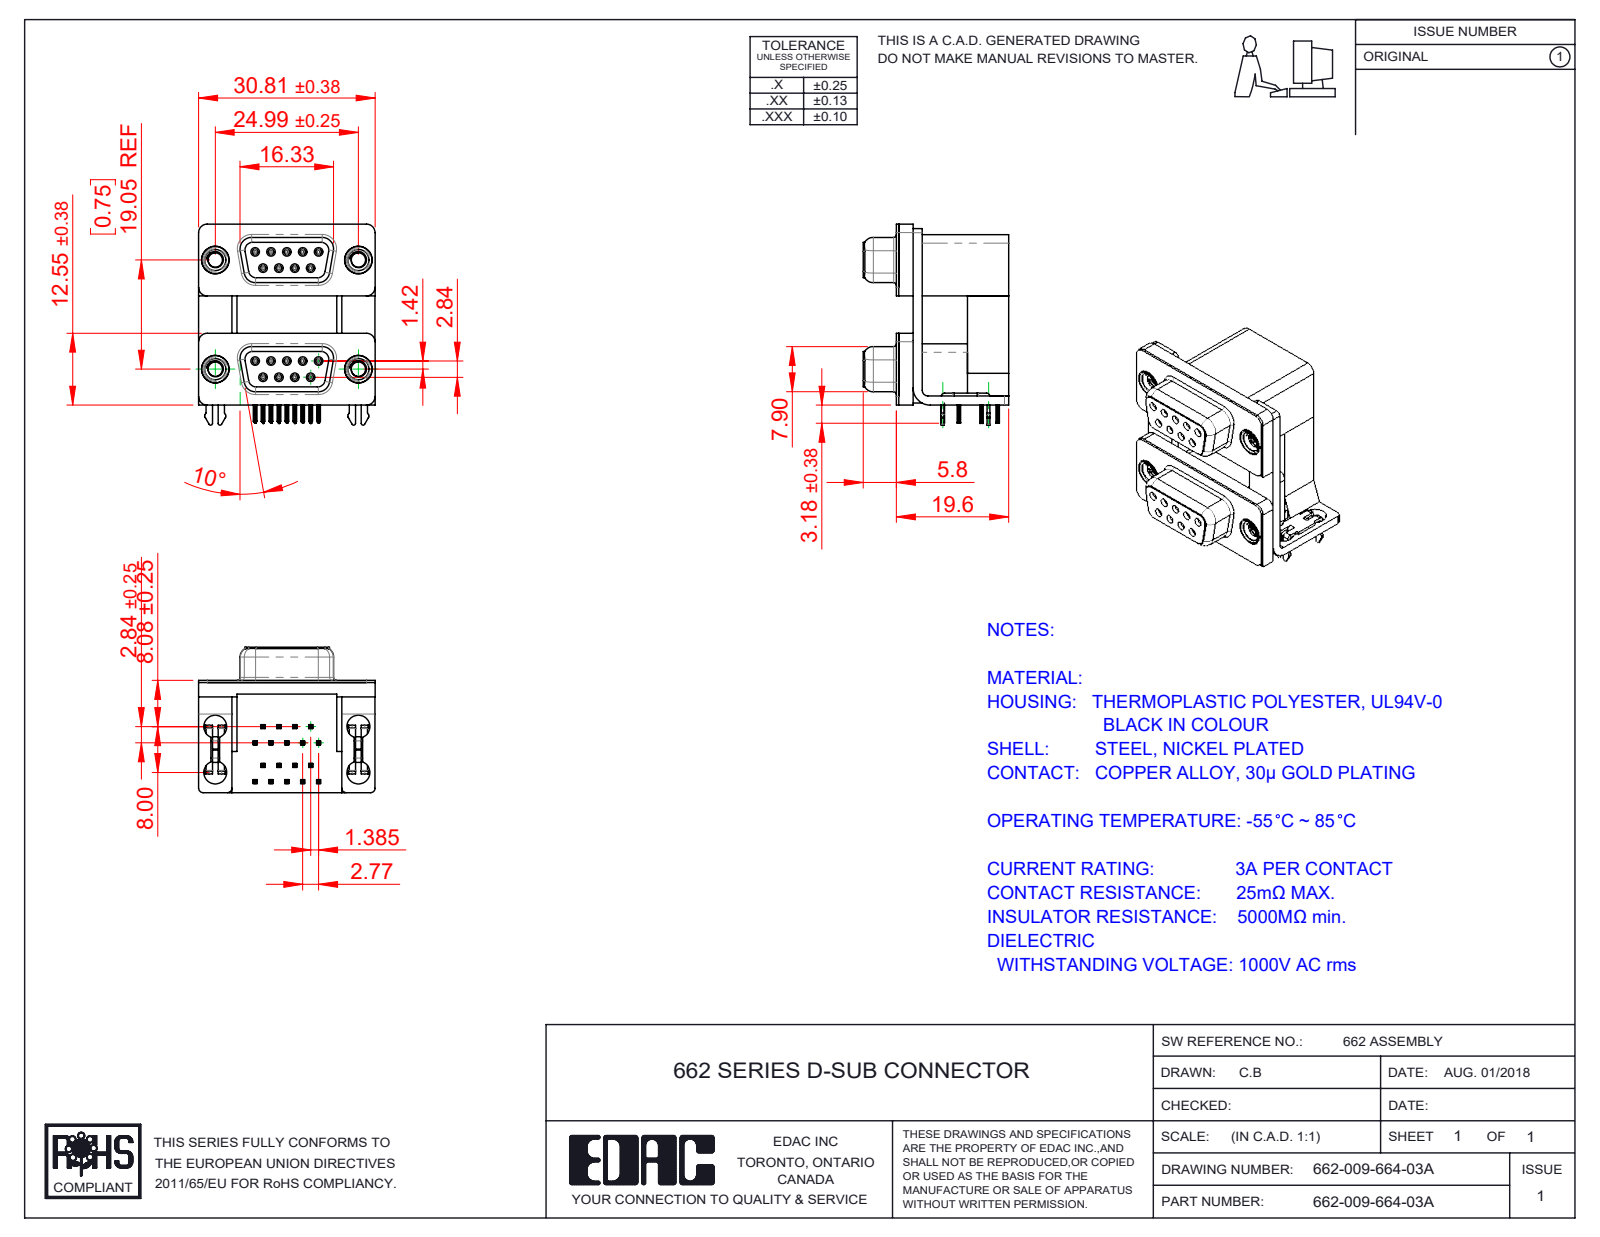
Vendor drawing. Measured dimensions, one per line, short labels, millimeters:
name: 662 Contact Bottom Upper_M; 662 Mounting Bracket_2ProngM; 662 2 Prong Board Lock_3; 662 Contact Top Upper_M (+8 more)
written by: SolidWorks 2020 (CONFIG_CONTROL_DESIGN)
unit: mm
bodies: 31 solids, 3266 faces (1476 planar, 854 cylindrical, 936 other)
size: 35.1 × 30.81 × 25.4
volume: 11 295 mm³; area: 13 472 mm²
holes: 18× ⌀0.8, 18× ⌀0.9, 8× ⌀4, 4× ⌀2.5, 4× ⌀3.5, 4× ⌀4.8, 4× ⌀5
bosses: 18× ⌀1.2, 4× ⌀4.9, 4× ⌀4.75, 4× ⌀3.9
rounds: 146× R0.1, 72× R0.15, 36× R0.35, 18× R0.34, 16× R1.35, 14× R1.5, 12× R0.5, 10× R0.25
face distances: 2.5, 0.4, 16.7, 19.2, 2.9, 19.05, 12, 12.4, 7.2, 9.5
hole spacings: 3.16, 19.25, 2.77, 19.05, 19.84, 21.93, 5.54, 22.28
